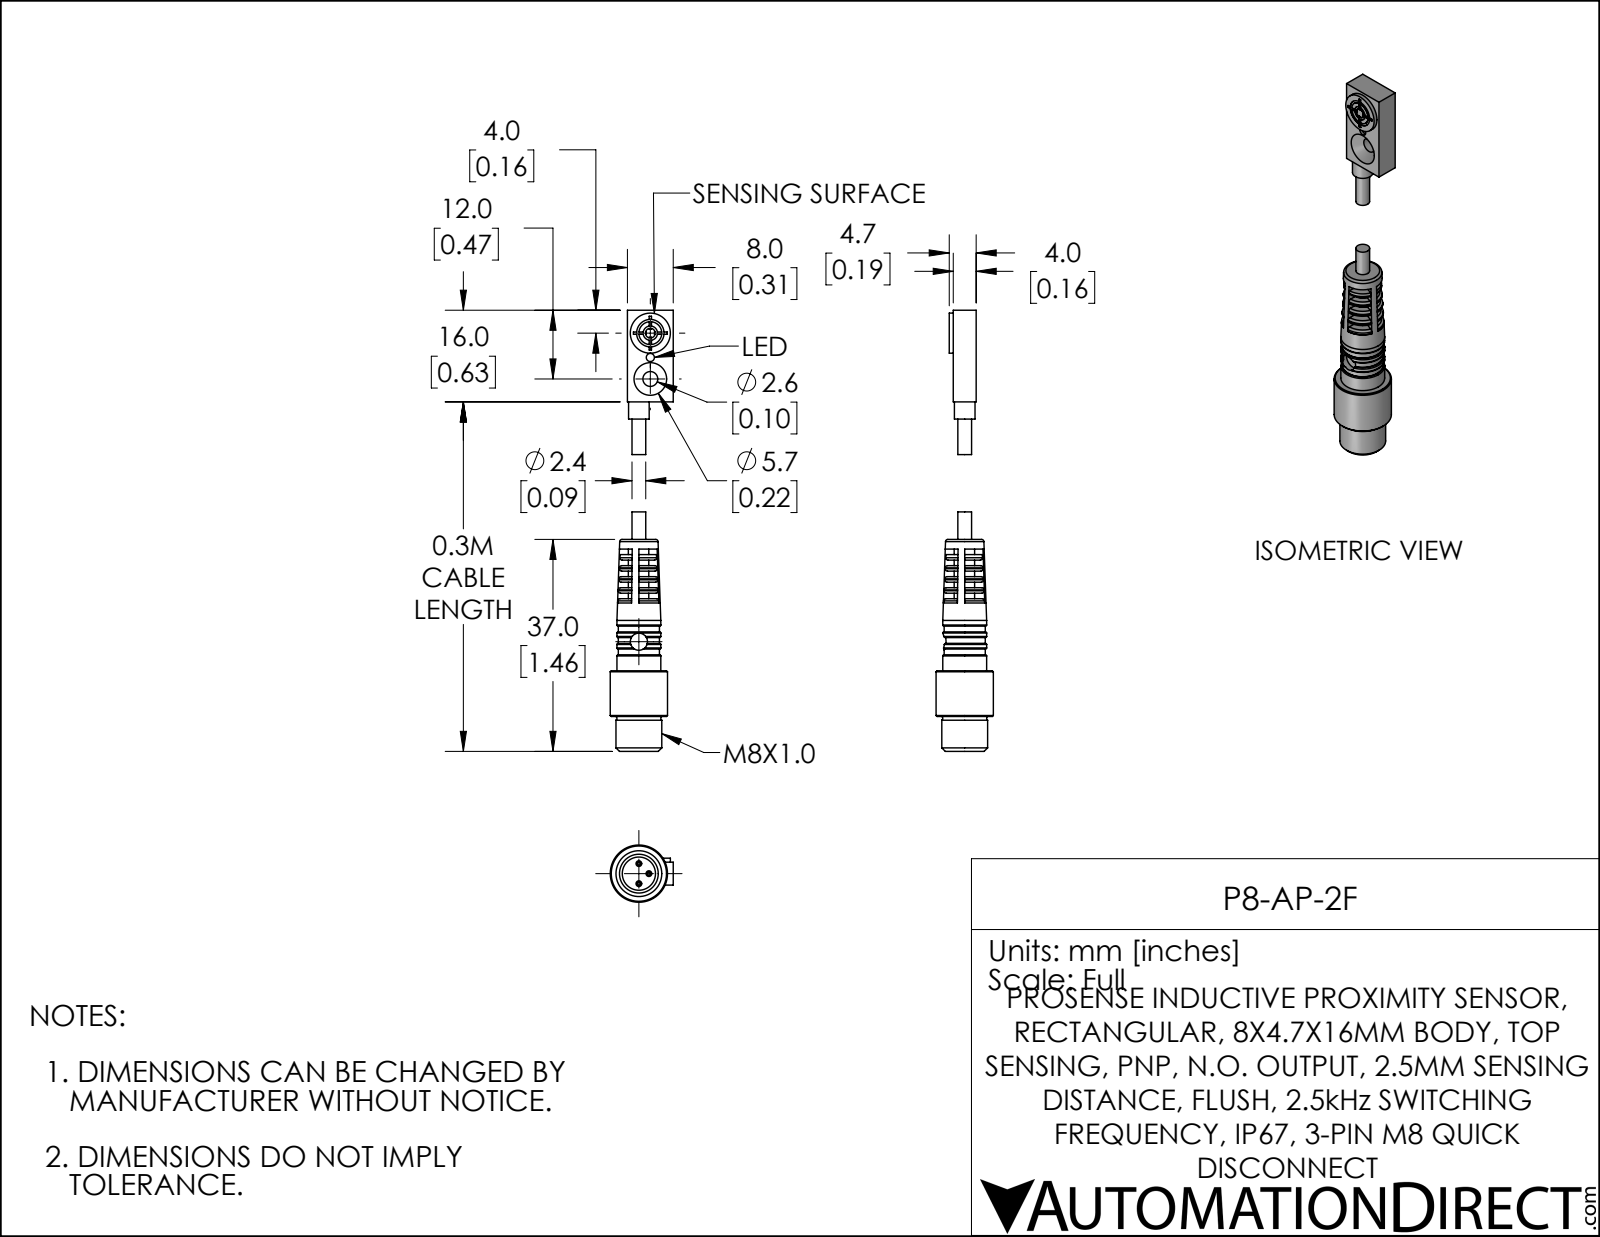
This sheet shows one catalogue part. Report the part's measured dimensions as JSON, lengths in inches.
{"part_name": "P8-AP-2F; P8-AP-2F_1; P8-AP-2F_2", "step_written_by": "SolidWorks 2019 (AUTOMOTIVE_DESIGN)", "units": "inches", "bodies": {"solids": 2, "faces": 240, "planar": 116, "cylindrical": 56, "other": 68}, "overall_size": [2.858, 0.433, 0.394], "volume_in3": 0.135, "surface_area_in2": 3.16, "round_holes": [[0.056, 1], [0.098, 1], [0.102, 1], [0.118, 1], [0.189, 1], [0.228, 1]], "round_bosses_or_shafts": [[0.039, 3], [0.394, 1], [0.315, 1], [0.302, 1], [0.283, 1], [0.276, 1], [0.157, 1], [0.142, 1]], "partial_cylinders_radius": [[0.033, 1], [0.072, 1]], "face_to_face_distances": [0.038, 0.152, 0.114, 0.315, 0.157, 0.076, 0.189, 0.076, 0.303, 0.265], "hole_center_spacings": [0.148, 0.167, 0.315]}
